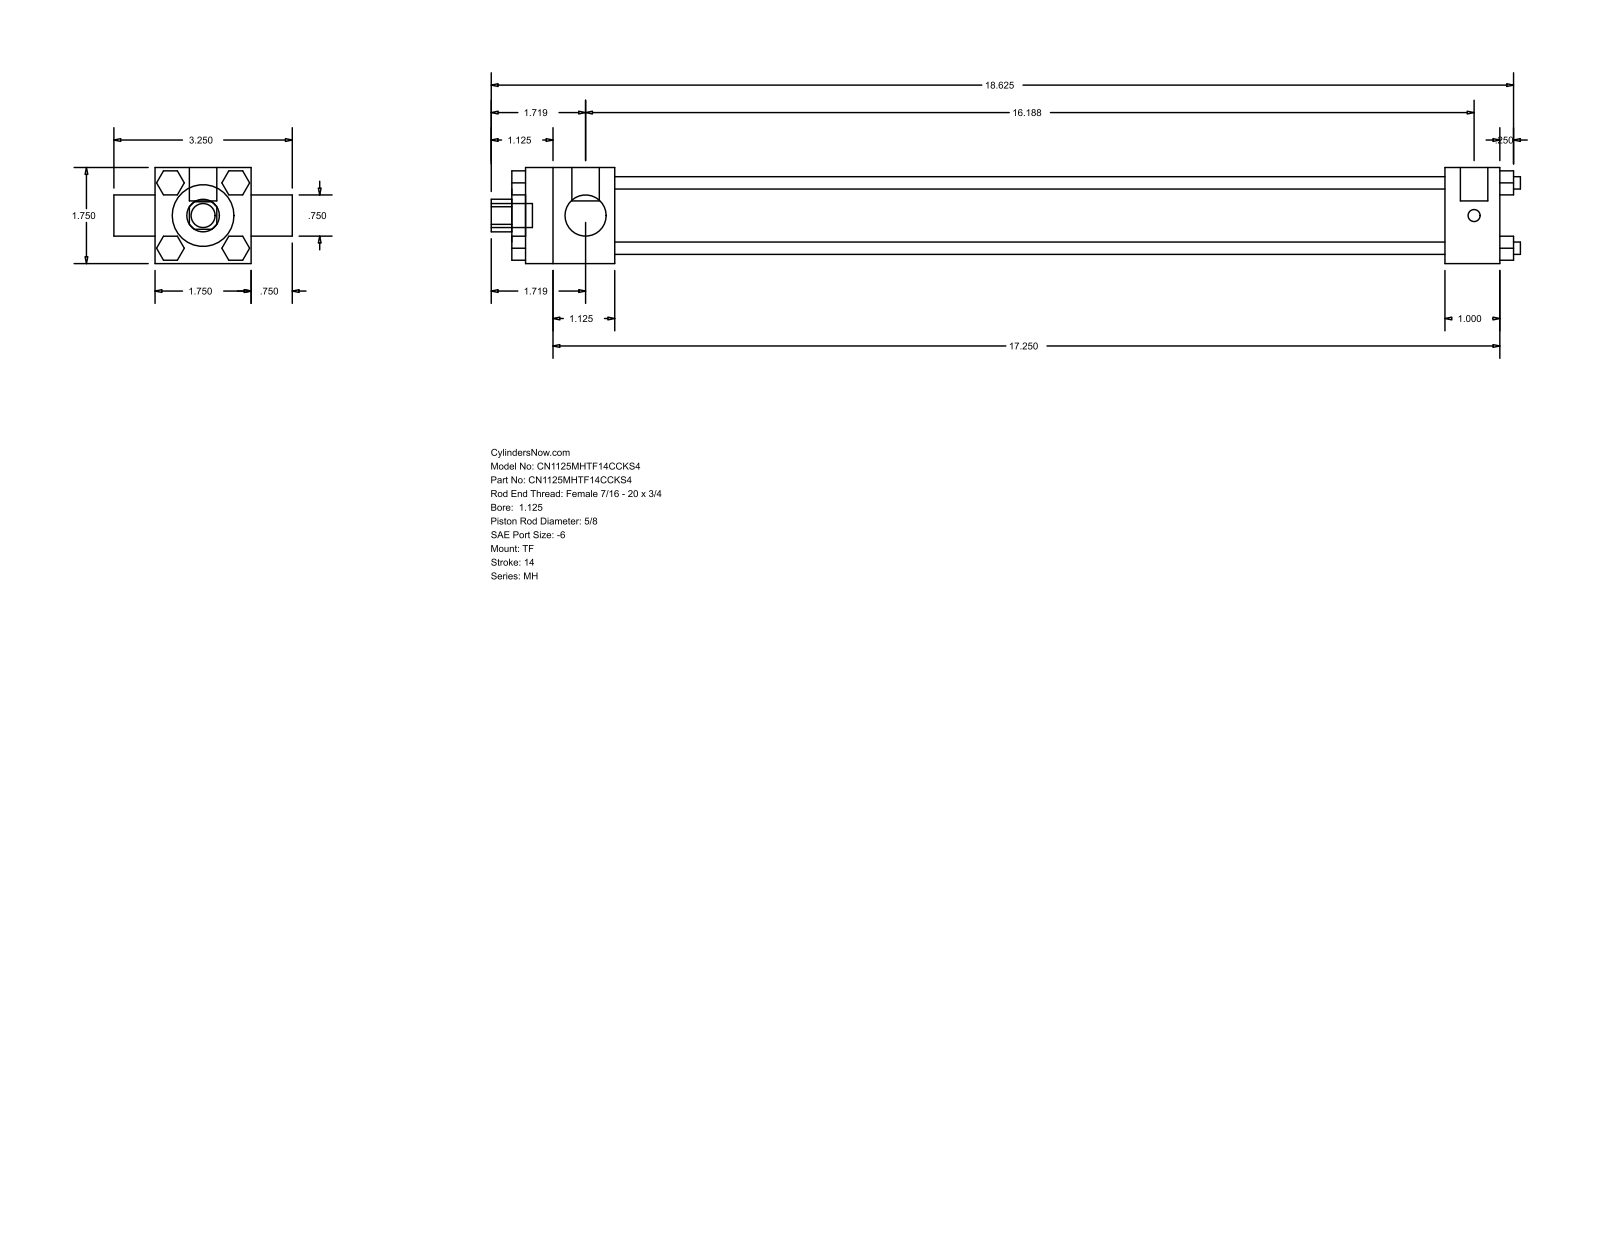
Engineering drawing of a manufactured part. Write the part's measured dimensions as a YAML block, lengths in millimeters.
part_name: "MH_TF__0112_0.625"
step_written_by: "GSSL Pune (CONFIG_CONTROL_DESIGN)"
units: millimeters
bodies: {solids: 0, faces: 120, planar: 92, cylindrical: 28, other: 0}
overall_size: [476.25, 82.55, 44.45]
round_holes:
  - {diameter: 15.88, count: 1}
  - {diameter: 19.05, count: 1}
  - {diameter: 28.57, count: 1}
  - {diameter: 34.92, count: 1}
round_bosses_or_shafts:
  - {diameter: 5.71, count: 4}
  - {diameter: 5.56, count: 3}
  - {diameter: 12.7, count: 2}
  - {diameter: 11.11, count: 1}
partial_cylinders:
  - {radius: 7.54, count: 1}
face_to_face_distances: [44.46, 11.11, 384.17, 409.58, 25.41, 41.27, 425.44, 450.85, 47.62, 457.2]
